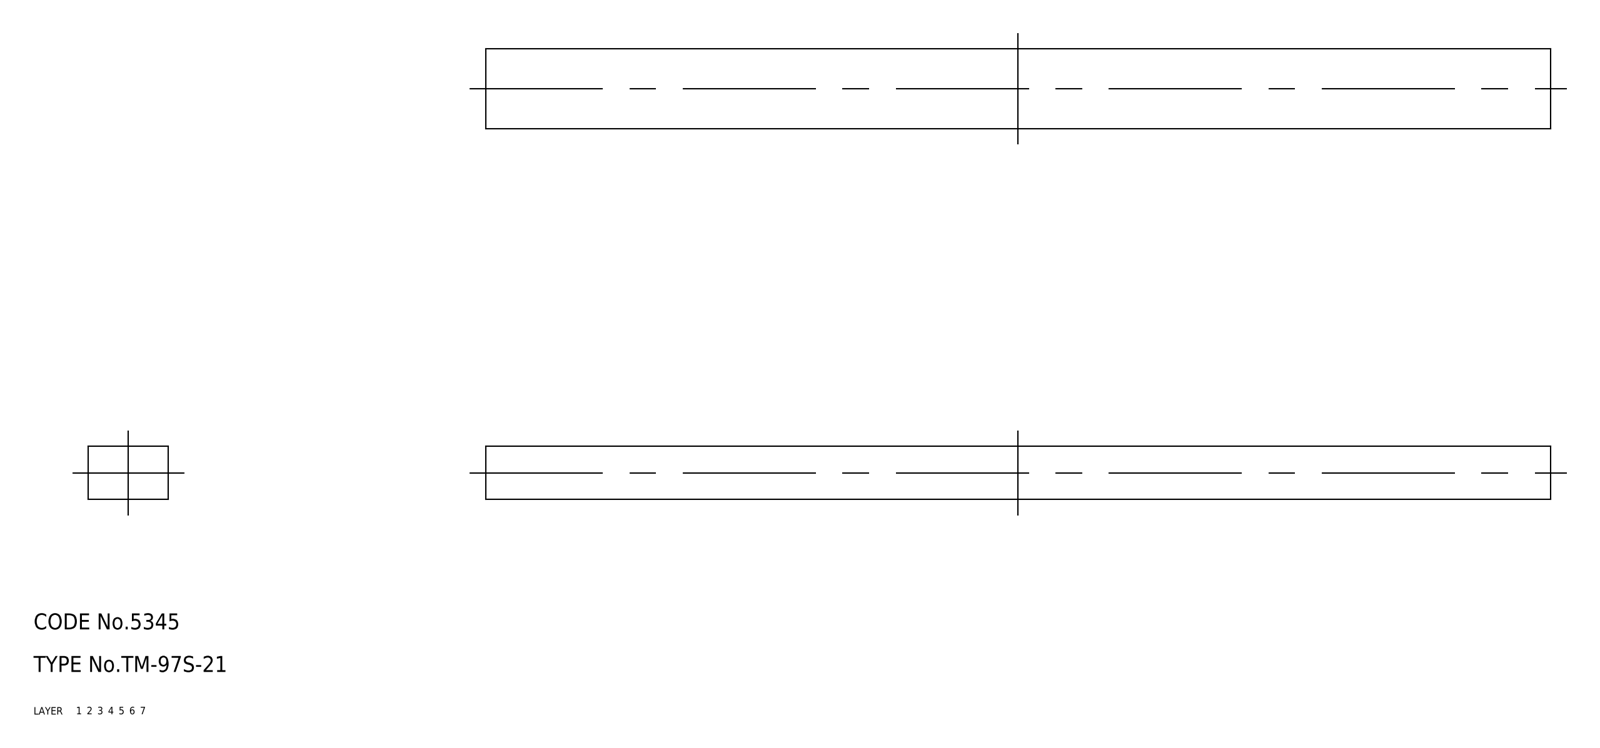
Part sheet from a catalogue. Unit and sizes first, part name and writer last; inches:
Units: inches
Overall size (bounding box): 7.874 × 0.591 × 0.394
Volume: 1.831 in³ · Surface area: 15.97 in²
Bodies: 1 solid, 6 faces (0 planar, 0 cylindrical, 6 other)
Part name (STEP PRODUCT): rubber foam
STEP written by: CADfix (AUTOMOTIVE_DESIGN)
